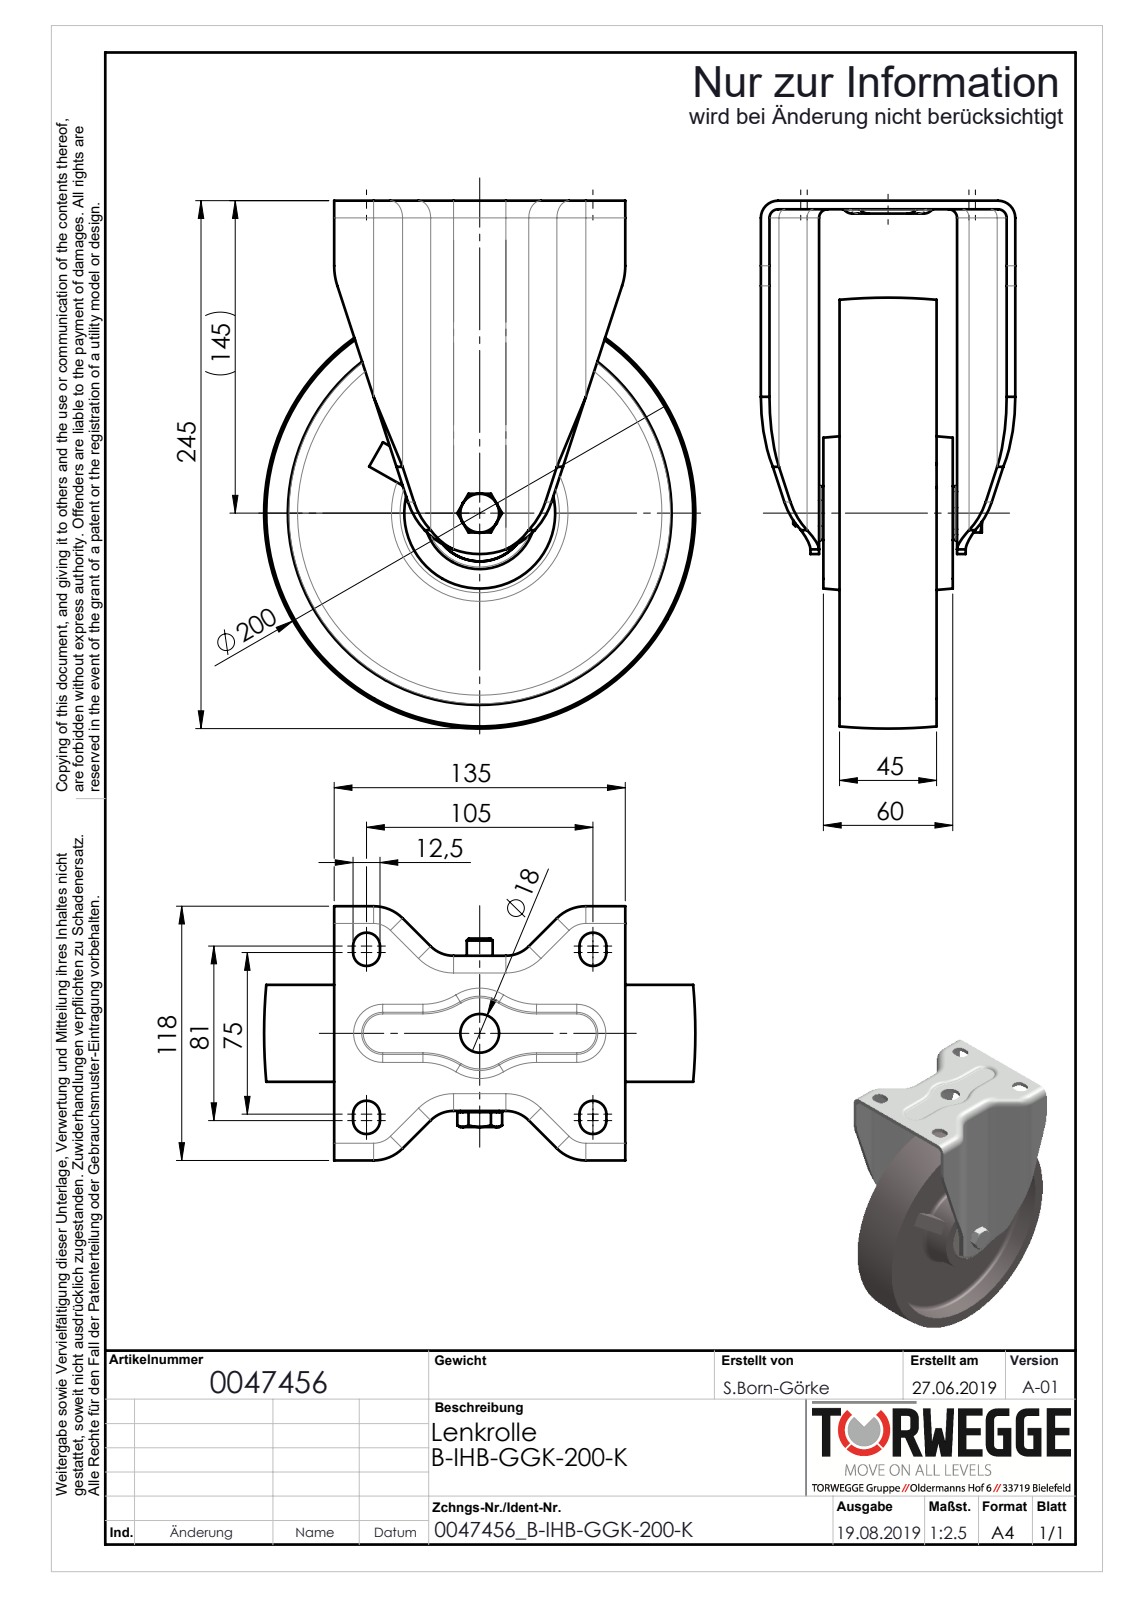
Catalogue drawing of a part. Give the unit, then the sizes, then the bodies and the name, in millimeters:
Units: millimetres
Overall size (bounding box): 245 × 200 × 118
Round holes (diameter × count): ⌀10.2 ×1, ⌀12 ×1, ⌀12.5 ×1, ⌀18 ×1, ⌀25 ×1, ⌀26 ×1, ⌀32.15 ×1, ⌀43.2 ×1, ⌀44.85 ×1, ⌀46 ×1, ⌀52 ×1
Round bosses / shafts (diameter × count): ⌀33.8 ×1, ⌀29 ×1, ⌀18 ×1
Partial cylindrical surfaces — rounded edges, fillets, slot ends (radius × count): R4 ×8, R6.25 ×8, R8 ×8, R15 ×8, R19 ×8, R1 ×4, R5 ×4, R30 ×2
Main face-to-face distances: 4, 8, 2, 18.5, 26.5, 40, 45, 7.5, 20.96, 6
Volume: 868 733 mm³ · Surface area: 275 186 mm²
Bodies: 16 solids, 418 faces (119 planar, 150 cylindrical, 149 other)
Part name (STEP PRODUCT): 0047456_B-IHB-GGK-200-K_(A-01)
STEP written by: SolidWorks 2018 (AUTOMOTIVE_DESIGN)
